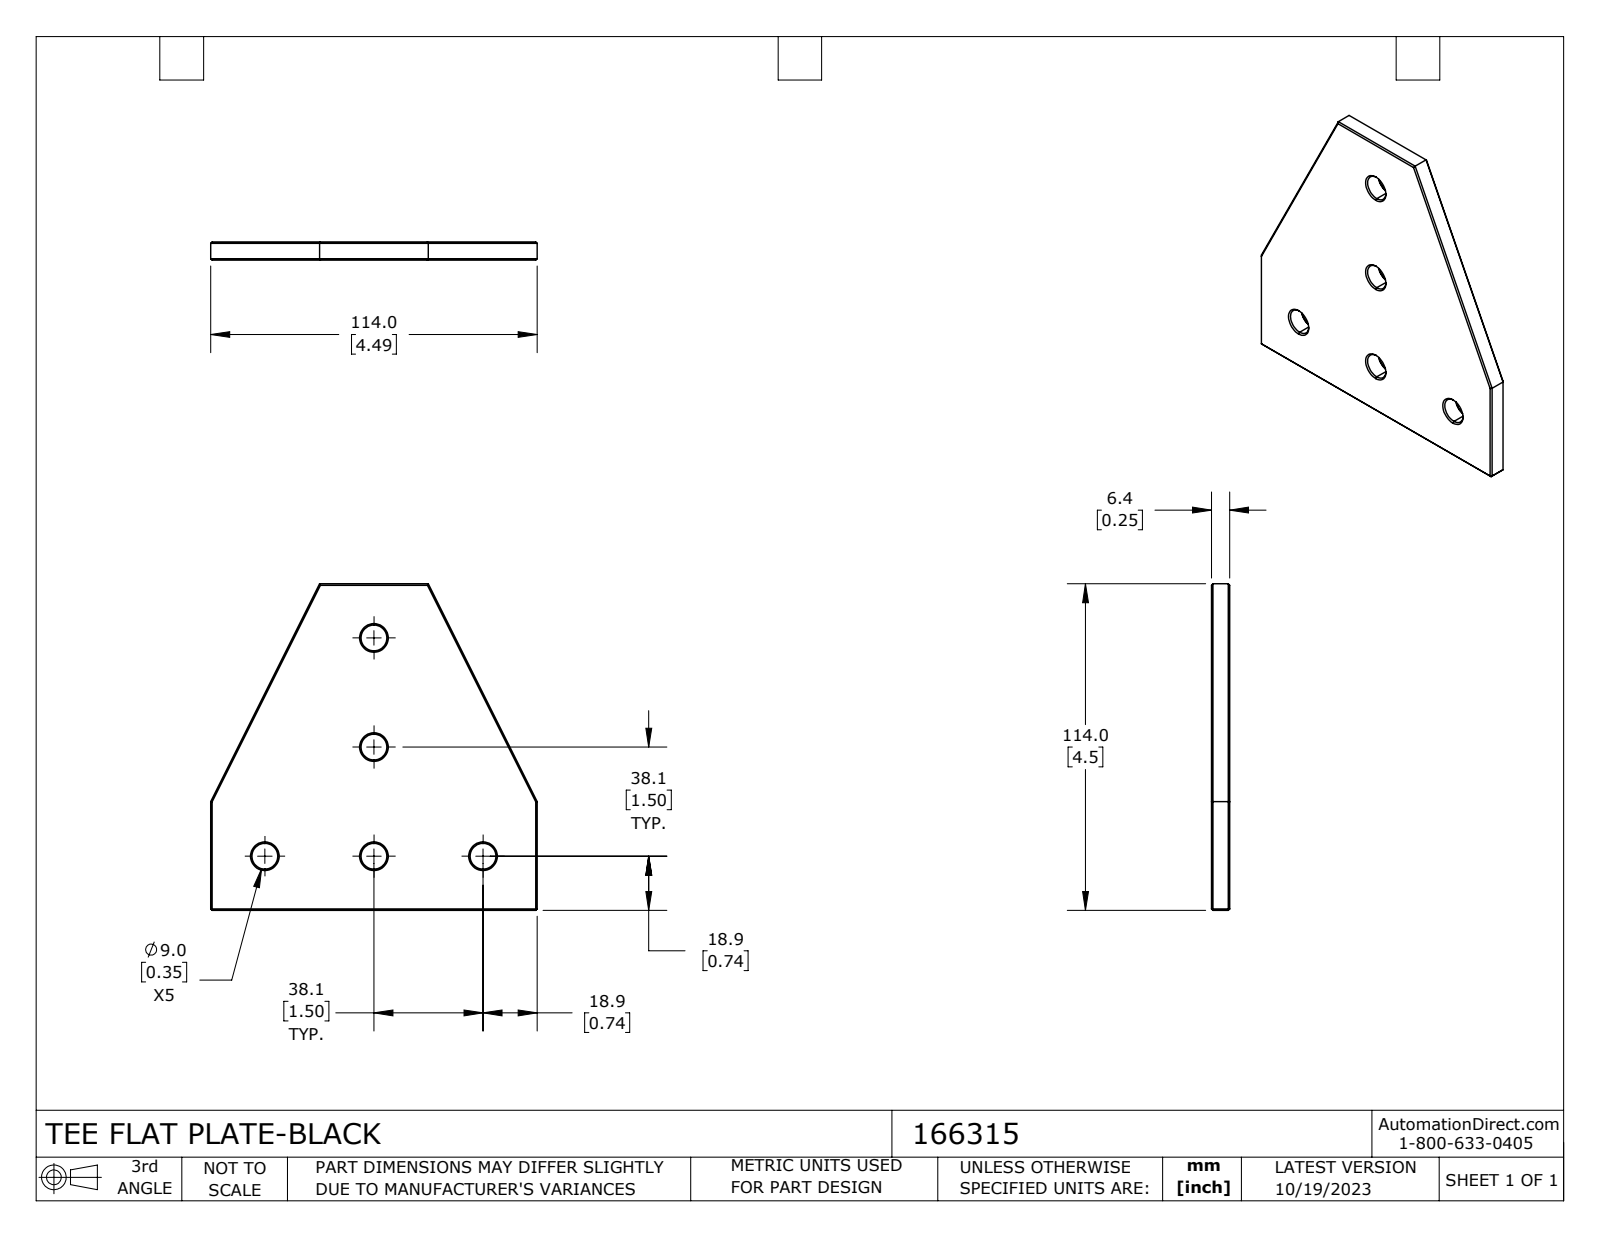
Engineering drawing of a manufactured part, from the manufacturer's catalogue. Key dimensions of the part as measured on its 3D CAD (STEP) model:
Part name (STEP PRODUCT): 166315
STEP written by: SolidWorks 2023 (CONFIG_CONTROL_DESIGN)
Units: millimetres
Bodies: 1 solid, 56 faces (26 planar, 10 cylindrical, 20 other)
Overall size (bounding box): 114 × 114 × 6.35
Volume: 62 029 mm³ · Surface area: 22 687 mm²
Round holes (diameter × count): ⌀9 ×5
Main face-to-face distances: 6.35, 114, 84.38
Hole centre spacings: 38.1, 53.88, 76.2, 85.19
